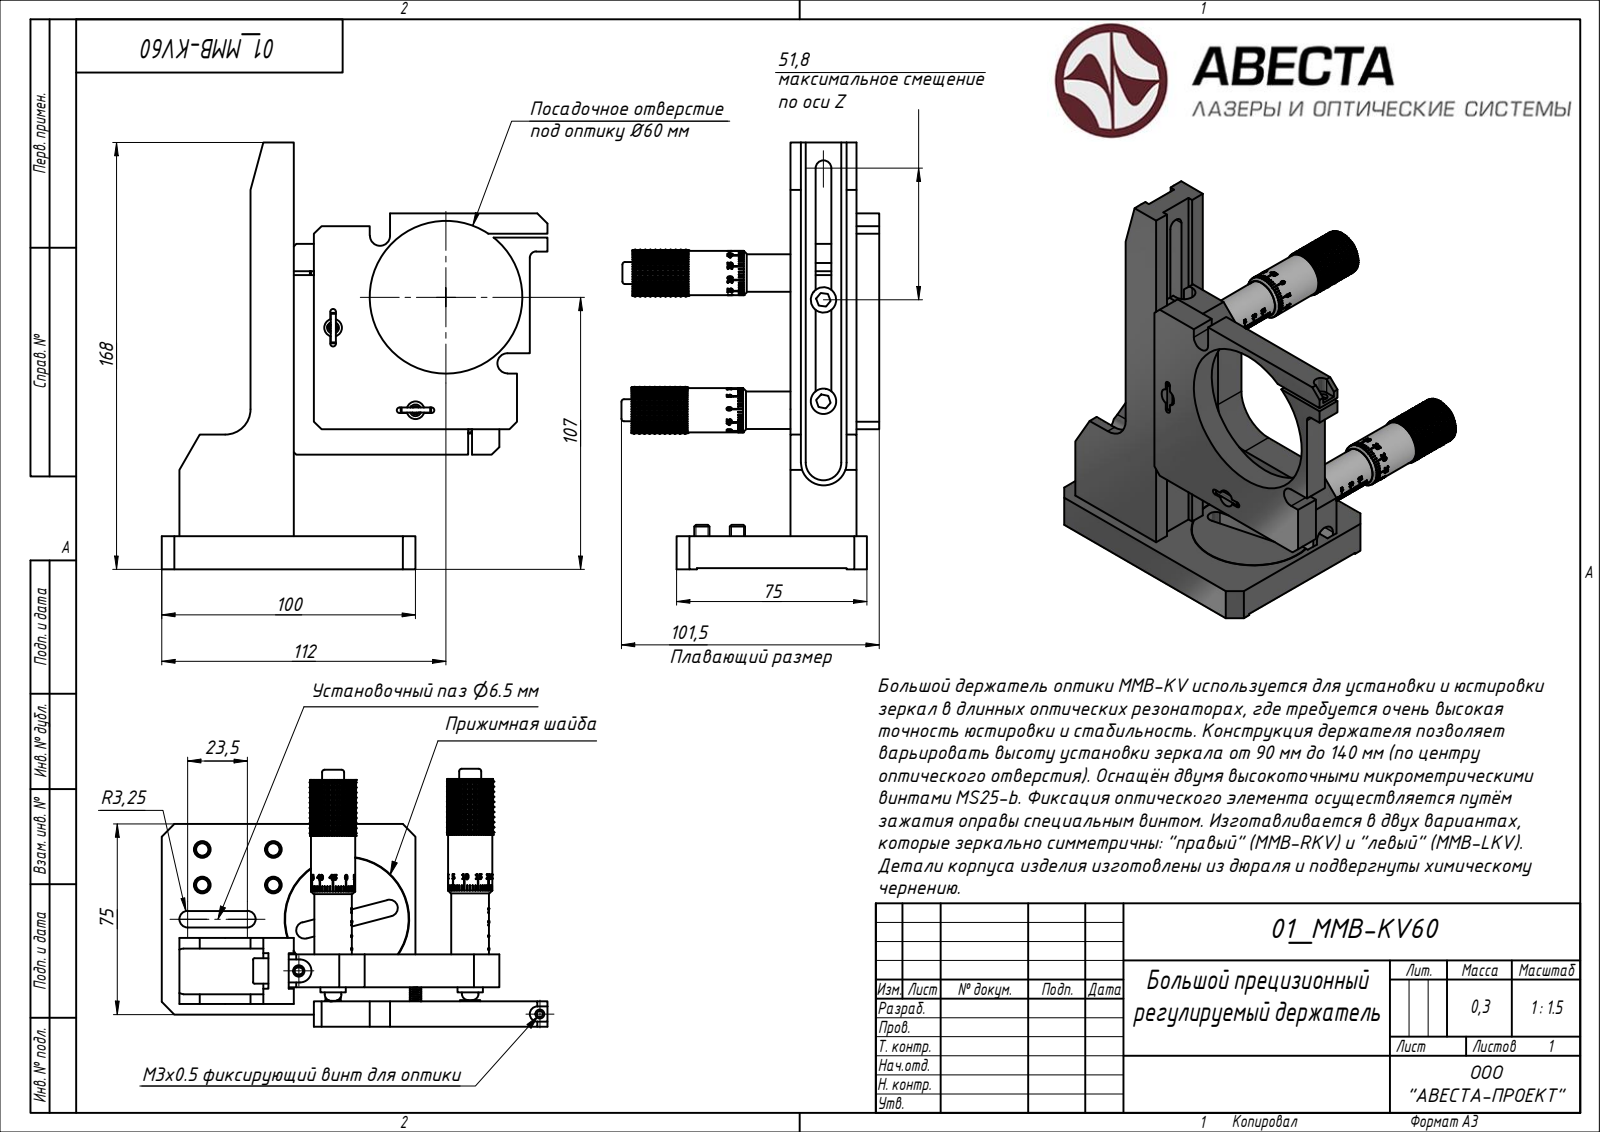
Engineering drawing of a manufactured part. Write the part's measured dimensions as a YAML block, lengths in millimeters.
step_written_by: "ST-DEVELOPER v15 (AUTOMOTIVE_DESIGN)"
units: millimeters
bodies: {solids: 16, faces: 410, planar: 173, cylindrical: 0, other: 237}
overall_size: [168, 152, 102.89]
volume: 260176
surface_area: 88719
face_to_face_distances: [10, 6.5, 19.5, 13, 26, 24.98, 34.98, 1.02, 8.98, 18.48]
